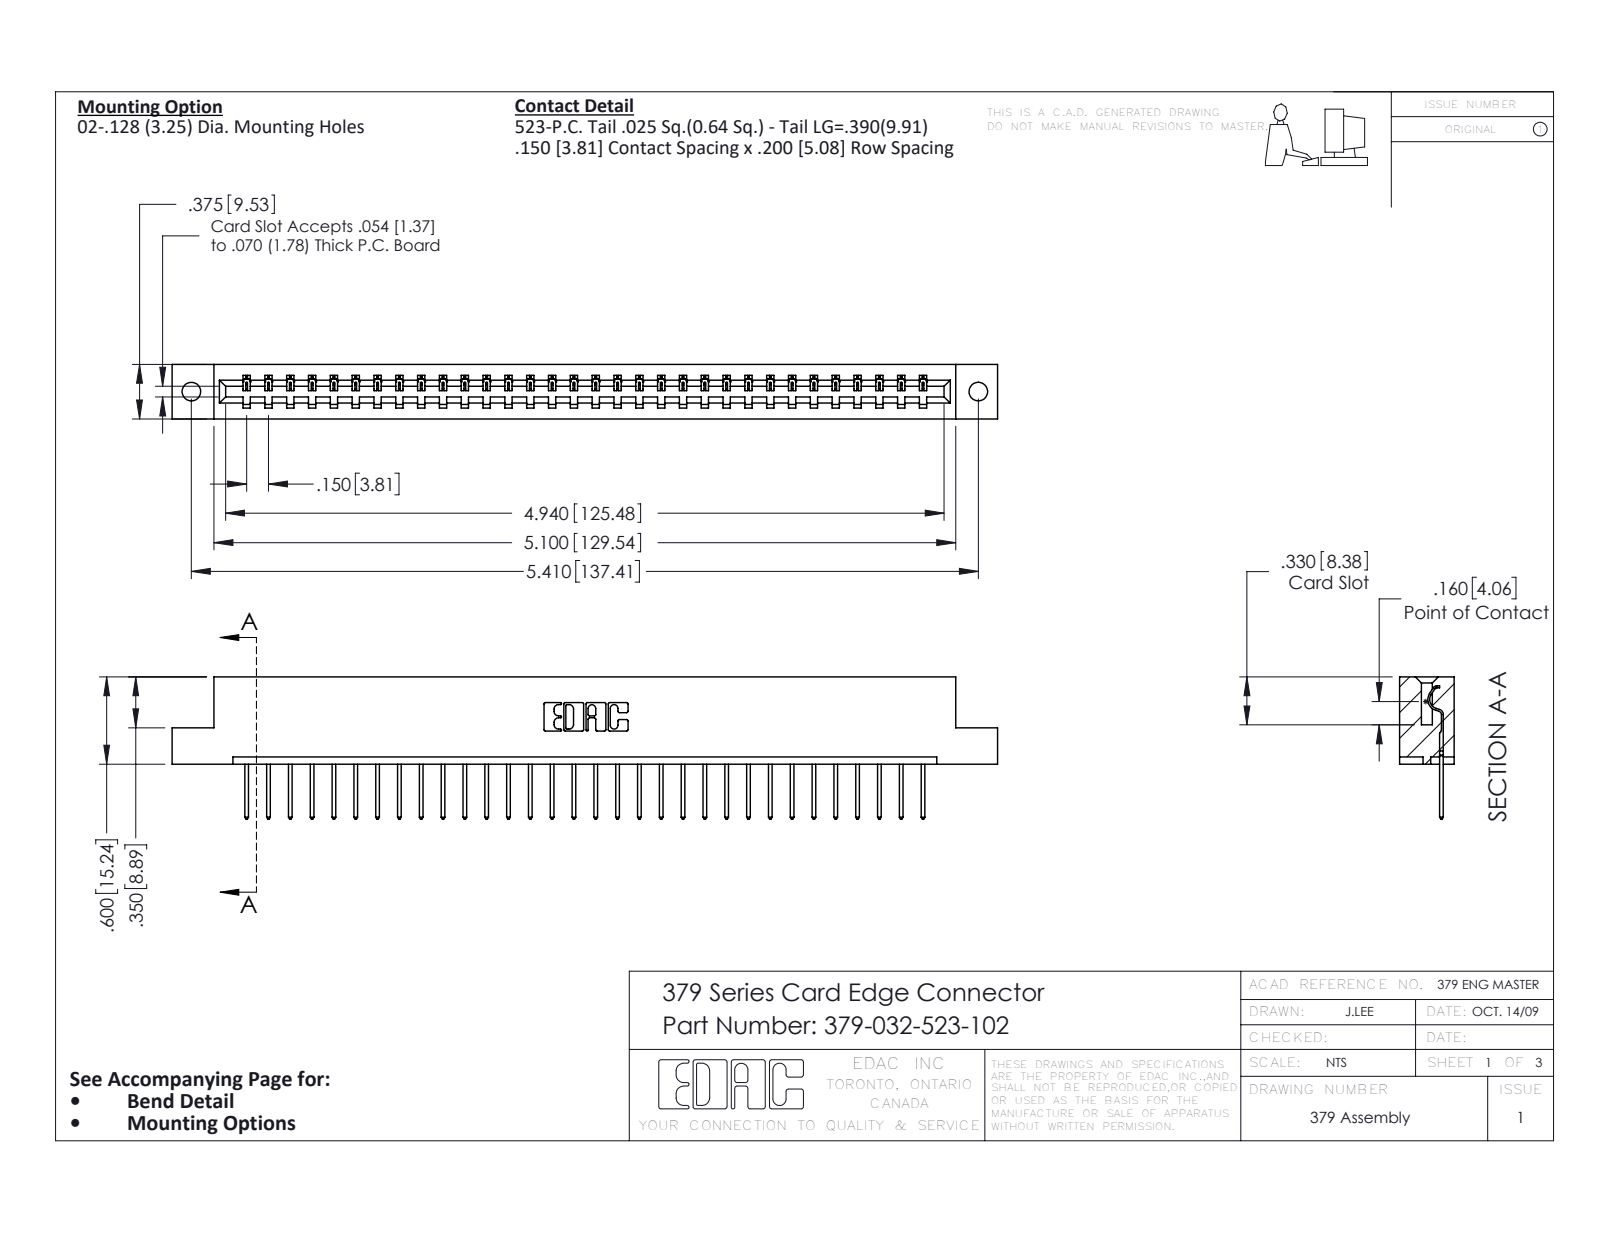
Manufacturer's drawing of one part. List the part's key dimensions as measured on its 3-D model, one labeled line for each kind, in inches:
Part name (STEP PRODUCT): 379-032-523-102; 345-292-001_345-293-123; 379 Part_Flush - .128 Dia
STEP written by: SolidWorks 2016 (CONFIG_CONTROL_DESIGN)
Units: inches
Bodies: 33 solids, 1970 faces (1414 planar, 556 cylindrical, 0 other)
Overall size (bounding box): 5.675 × 0.977 × 0.375
Volume: 0.914 in³ · Surface area: 23.3 in²
Round holes (diameter × count): ⌀0.128 ×2
Partial cylindrical surfaces — rounded edges, fillets, slot ends (radius × count): R0.006 ×64, R0.01 ×64, R0.01 ×22, R0.007 ×6, R0.031 ×6, R0.026 ×3, R0.014 ×1, R0.022 ×1
Main face-to-face distances: 0.3, 0.075, 0.375, 0.225, 0.2, 0.6, 0.275, 0.1, 0.025, 0.55
Hole centre spacings: 5.41
